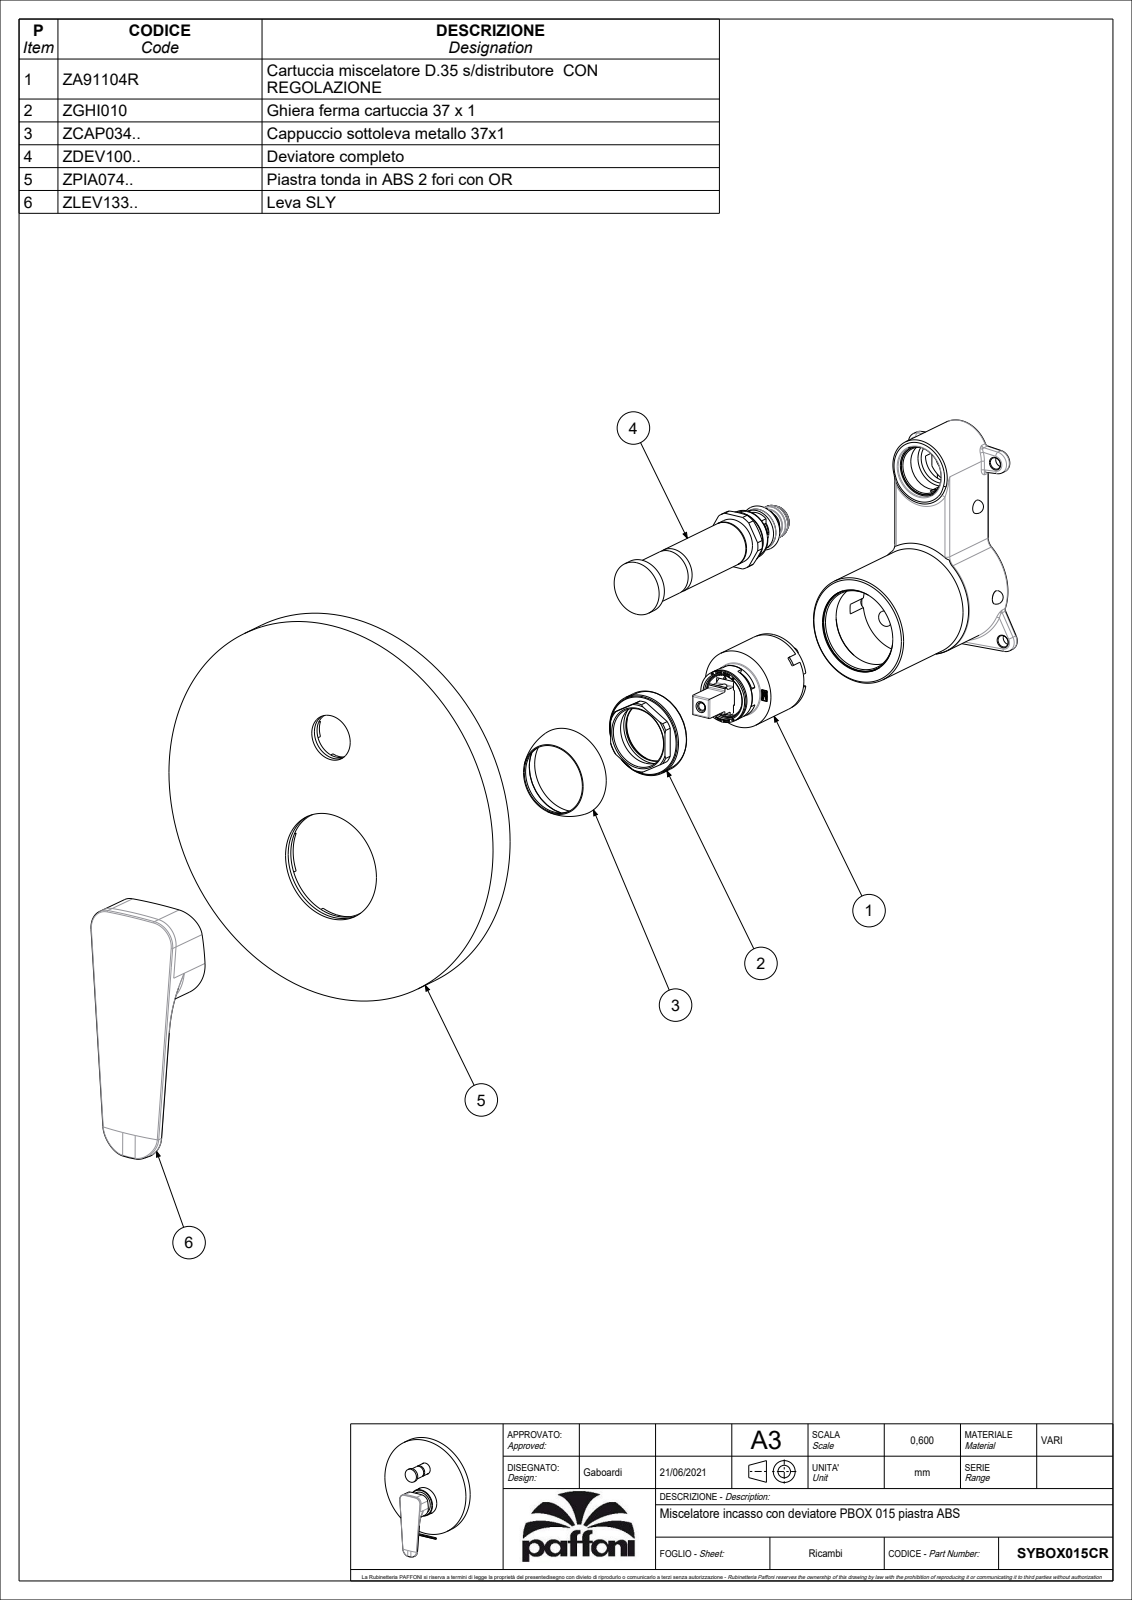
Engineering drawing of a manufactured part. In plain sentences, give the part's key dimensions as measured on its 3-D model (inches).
The part is named "SYBOX015CR". Its 3-D file was written by "CREO PARAMETRIC BY PTC INC, 2020044 (CONFIG_CONTROL_DESIGN)". It is 5 solids with 1057 faces: 620 planar, 258 cylindrical and 179 other. Overall it measures 7.963 by 6.811 by 2.417 inches. Its volume is 14.64 cubic inches and its surface area 187.1 square inches. Round holes: 2 of diameter 0.13, 2 of diameter 0.157, 1 of diameter 0.118, 1 of diameter 0.177, 1 of diameter 0.197, 1 of diameter 0.28, 1 of diameter 0.63, 1 of diameter 0.717, 1 of diameter 0.768, 1 of diameter 0.783, 1 of diameter 0.807, 1 of diameter 0.984. Round bosses or shafts: 1 of diameter 6.811, 1 of diameter 6.575, 1 of diameter 2.244, 1 of diameter 1.894, 1 of diameter 1.378, 1 of diameter 1.142, 1 of diameter 0.945, 1 of diameter 0.925. Partial cylindrical surfaces (rounded edges, fillets, slot ends): 27 of radius 0.02, 11 of radius 0.006, 4 of radius 0.012, 4 of radius 0.059, 2 of radius 0.039, 2 of radius 0.394, 1 of radius 0.098, 1 of radius 0.177. The main face-to-face distances are 0.512, 0.079, 0.433, 0.256, 2.24, 1.807, 1.728, 0.177, 0.394, 2.228. The hole center spacings are 0.433, 1.014, 1.348, 2.362.
